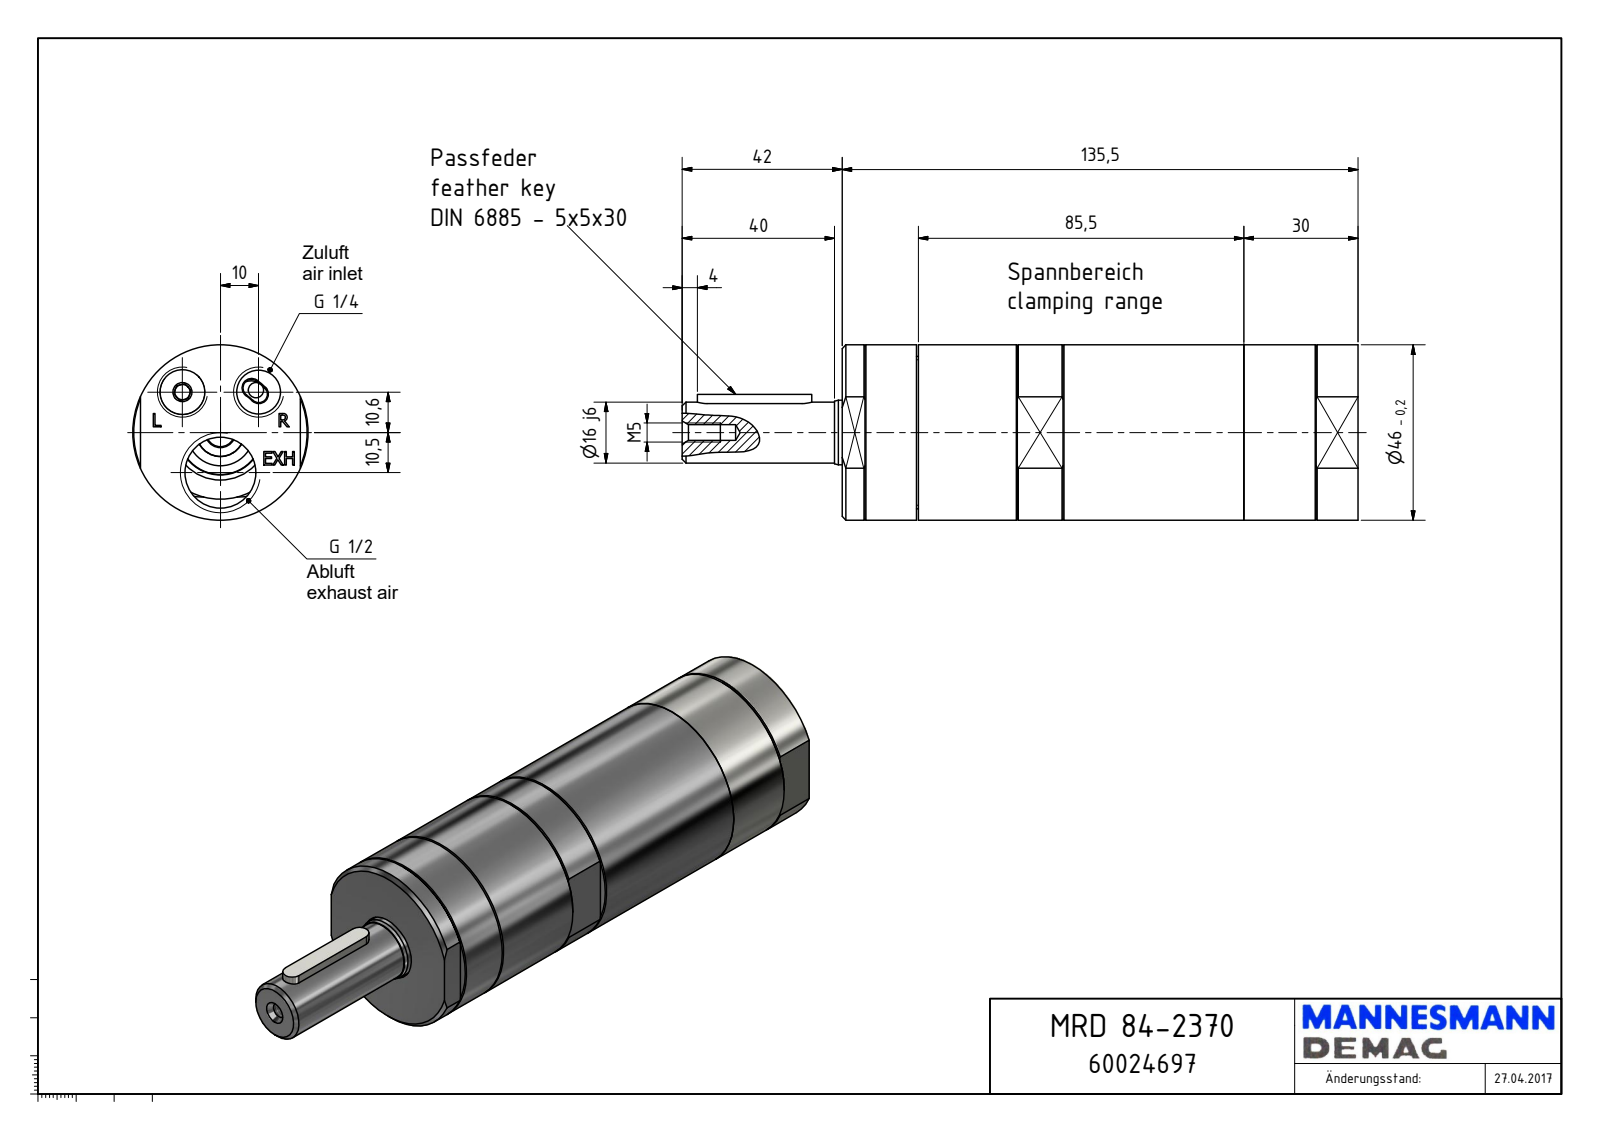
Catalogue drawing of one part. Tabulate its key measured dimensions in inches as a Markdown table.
| quantity | value |
| --- | --- |
| part name | Bauteil3 |
| STEP written by | Autodesk Inventor 2018 (AUTOMOTIVE_DESIGN) |
| units | inches |
| bodies | 1 solid, 182 faces (110 planar, 36 cylindrical, 36 other) |
| overall size | 8.366 × 1.811 × 1.811 |
| volume | 17.41 in³ |
| surface area | 52.94 in² |
| round holes (diameter × count) | 0.157 × 1, 0.163 × 1, 0.451 × 1, 0.689 × 1, 0.733 × 1, 1.496 × 1, 1.511 × 1 |
| round bosses / shafts (diameter × count) | 1.811 × 1, 1.328 × 1, 0.667 × 1, 0.63 × 1 |
| partial cylindrical surfaces (radius × count) | 0.098 × 2, 0.197 × 2, 0.225 × 1, 0.259 × 1, 0.354 × 1 |
| main face-to-face distances | 6.713, 1.654, 6.387, 0.325, 0.787, 5.6, 5.925, 0.768, 0.02, 5.62 |
| hole center spacings | 0.574, 0.919, 0.413, 0.787 |
